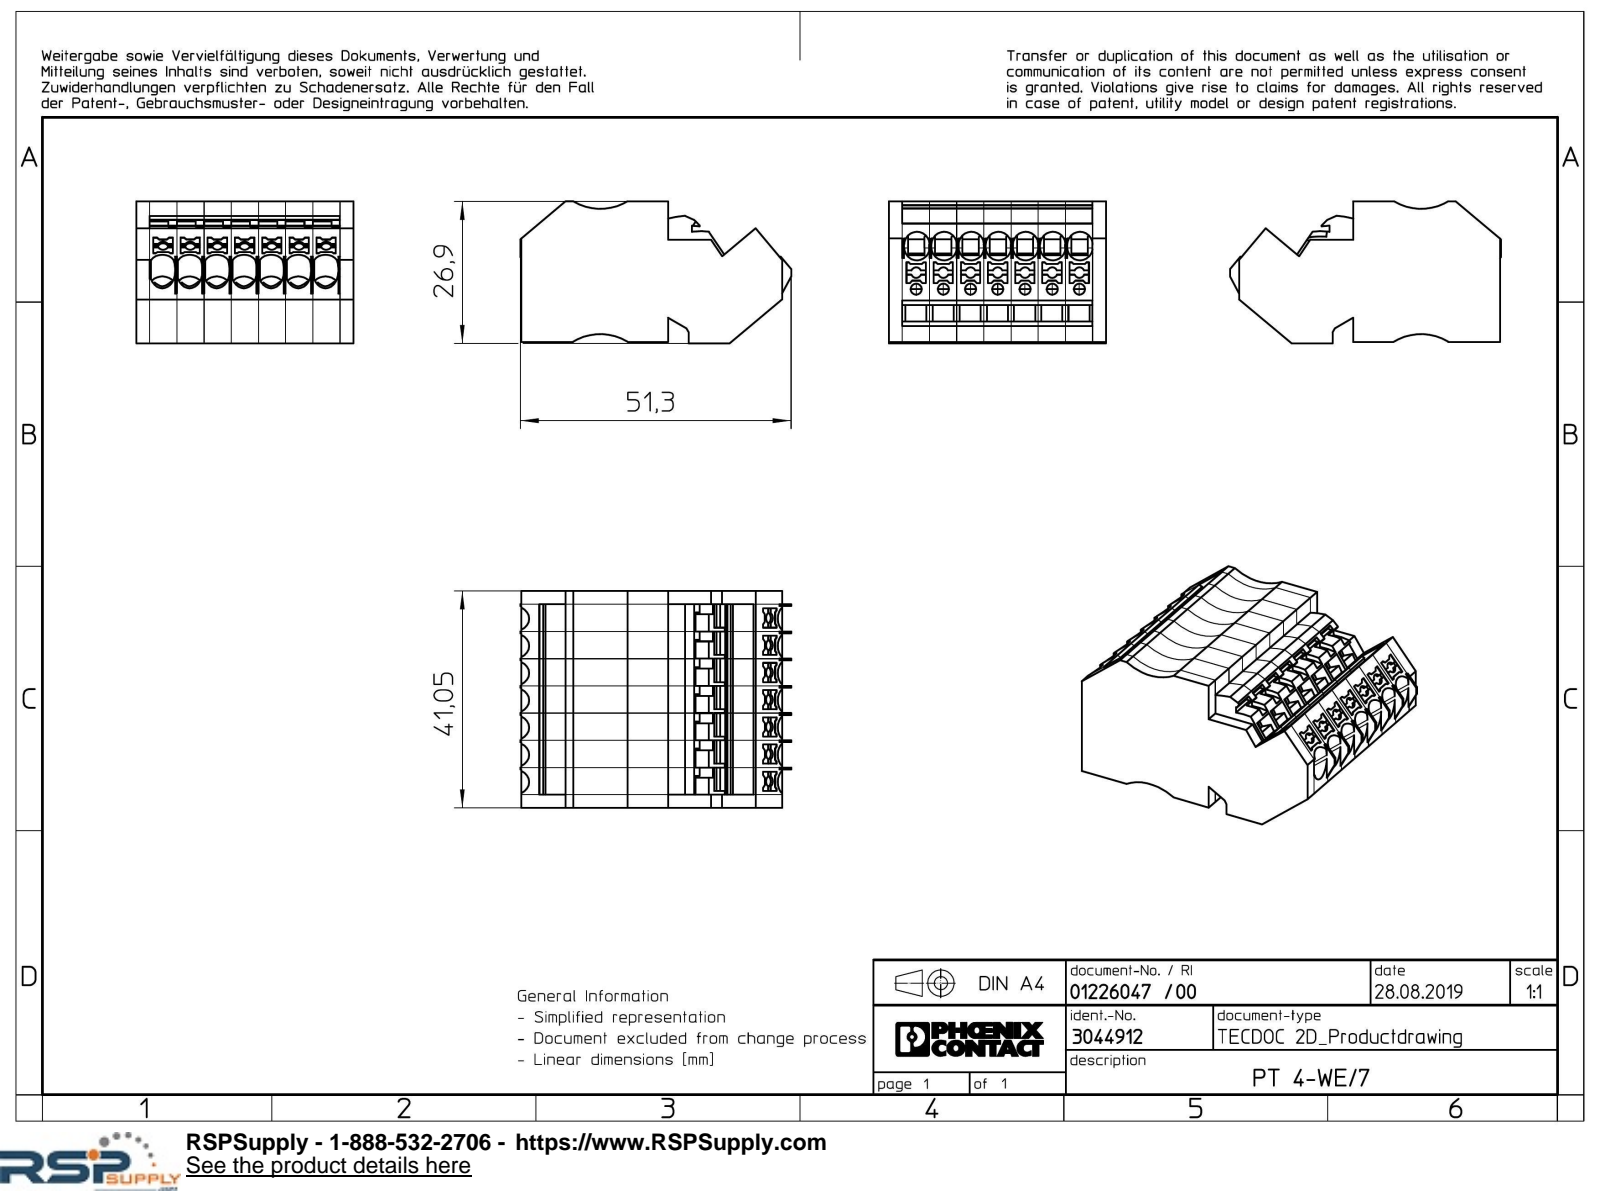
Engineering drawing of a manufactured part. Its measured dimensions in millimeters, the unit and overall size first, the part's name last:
Units: millimetres
Overall size (bounding box): 51.3 × 41.05 × 26.9
Round holes (diameter × count): ⌀2.1 ×7
Partial cylindrical surfaces — rounded edges, fillets, slot ends (radius × count): R2.4 ×28, R1 ×14, R1.03 ×3, R10 ×2, R1.05 ×1, R1.78 ×1, R12.4 ×1, R13.38 ×1
Main face-to-face distances: 41.05, 5.15, 10.3, 15.45, 7.2, 3.15, 3.85, 7, 3.1, 19.6
Hole centre spacings: 5.15, 10.3, 15.45, 20.6, 25.75, 30.9
Volume: 37 358 mm³ · Surface area: 14 943 mm²
Bodies: 1 solid, 1199 faces (1041 planar, 144 cylindrical, 14 other)
Part name (STEP PRODUCT): PT_4_WE_7-select
STEP written by: Creo Elements/Direct Modeling 20.1A 29-Sep-2018 (C) Parametric Technology GmbH (AUTOMOTIVE_DESIGN)
